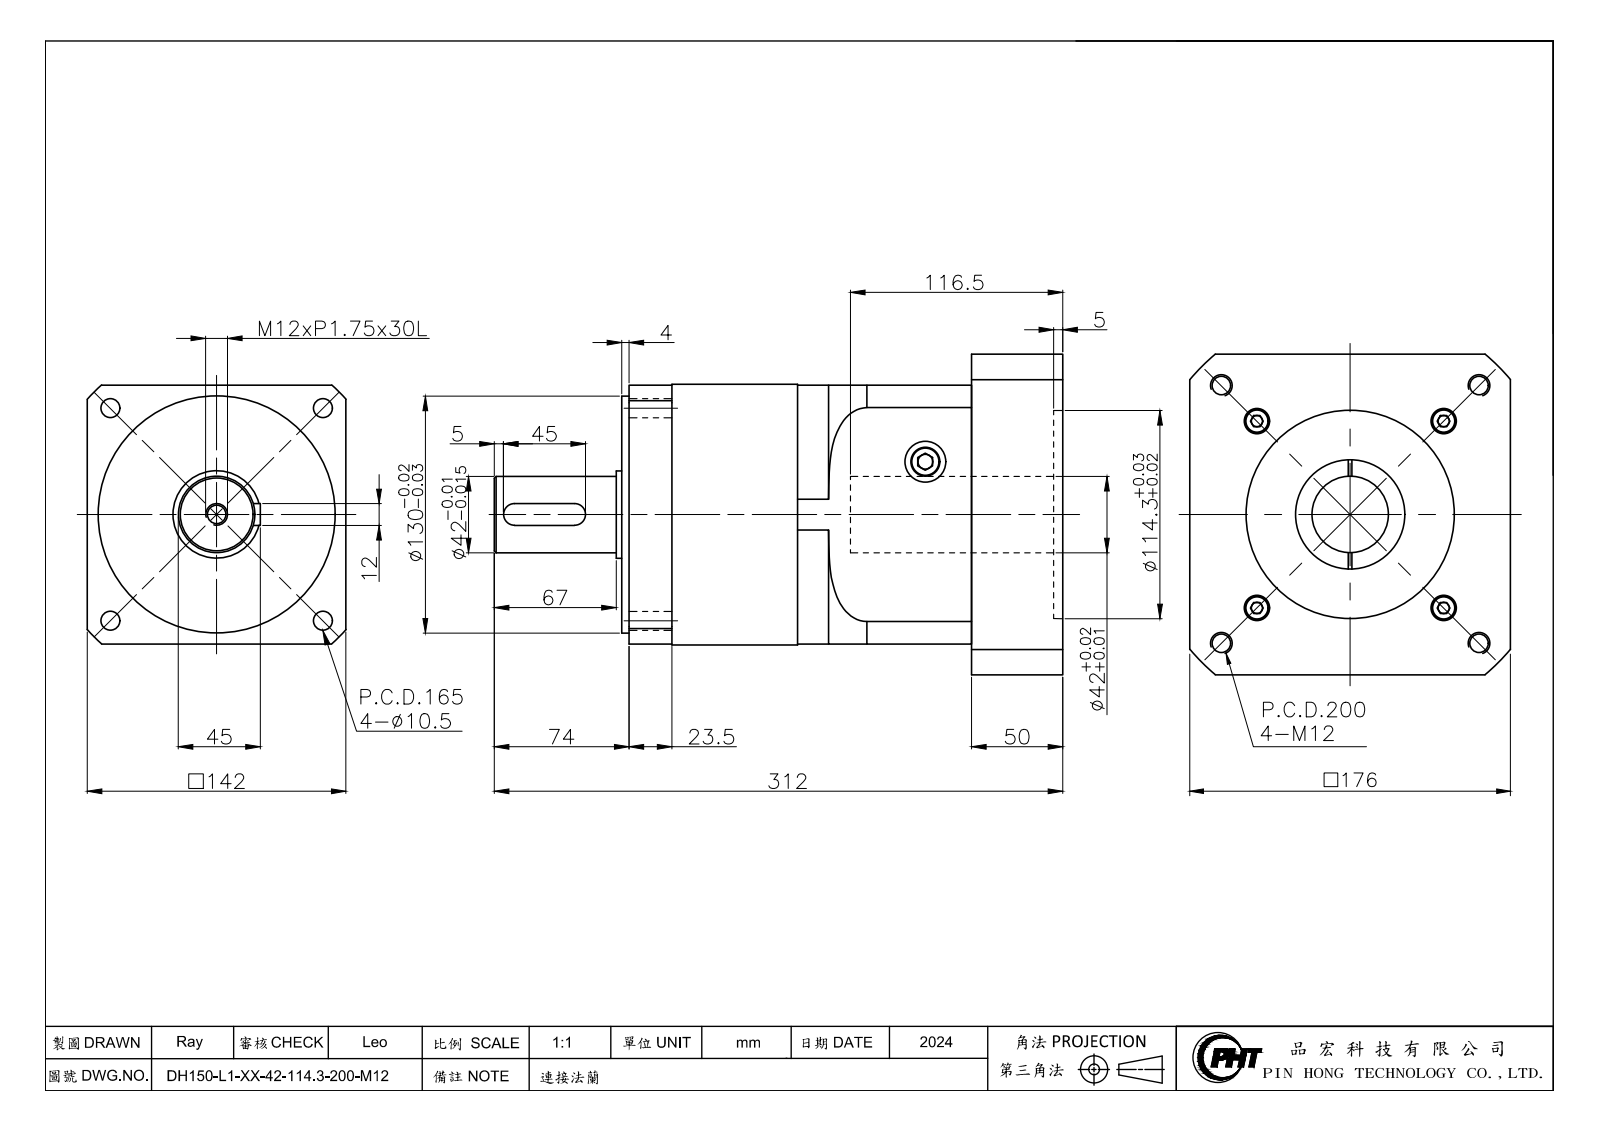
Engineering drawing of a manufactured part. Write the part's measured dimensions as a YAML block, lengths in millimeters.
part_name: "DH150-L1-3-35-114.3-200-M12(連接法蘭)_2024AAA"
step_written_by: "SolidWorks 2016 (CONFIG_CONTROL_DESIGN)"
units: millimeters
bodies: {solids: 6, faces: 353, planar: 164, cylindrical: 141, other: 48}
overall_size: [312, 176, 176]
volume: 4515000
surface_area: 344559
round_holes:
  - {diameter: 14, count: 8}
  - {diameter: 10.2, count: 5}
  - {diameter: 6.8, count: 4}
  - {diameter: 9, count: 4}
  - {diameter: 10.5, count: 4}
  - {diameter: 15, count: 4}
  - {diameter: 22.5, count: 2}
  - {diameter: 42, count: 1}
  - {diameter: 60, count: 1}
  - {diameter: 92, count: 1}
  - {diameter: 110, count: 1}
  - {diameter: 114.3, count: 1}
round_bosses_or_shafts:
  - {diameter: 12.2, count: 12}
  - {diameter: 8, count: 4}
  - {diameter: 143, count: 1}
  - {diameter: 130, count: 1}
  - {diameter: 74, count: 1}
  - {diameter: 48, count: 1}
partial_cylinders:
  - {radius: 6, count: 2}
  - {radius: 72, count: 1}
  - {radius: 92.5, count: 1}
  - {radius: 95, count: 1}
  - {radius: 115, count: 1}
face_to_face_distances: [17, 159, 142, 50, 176, 192, 242, 5, 56, 4]
hole_center_spacings: [66, 19.2, 25.37, 40.07, 84.48, 91.35, 93.34, 104.59]
